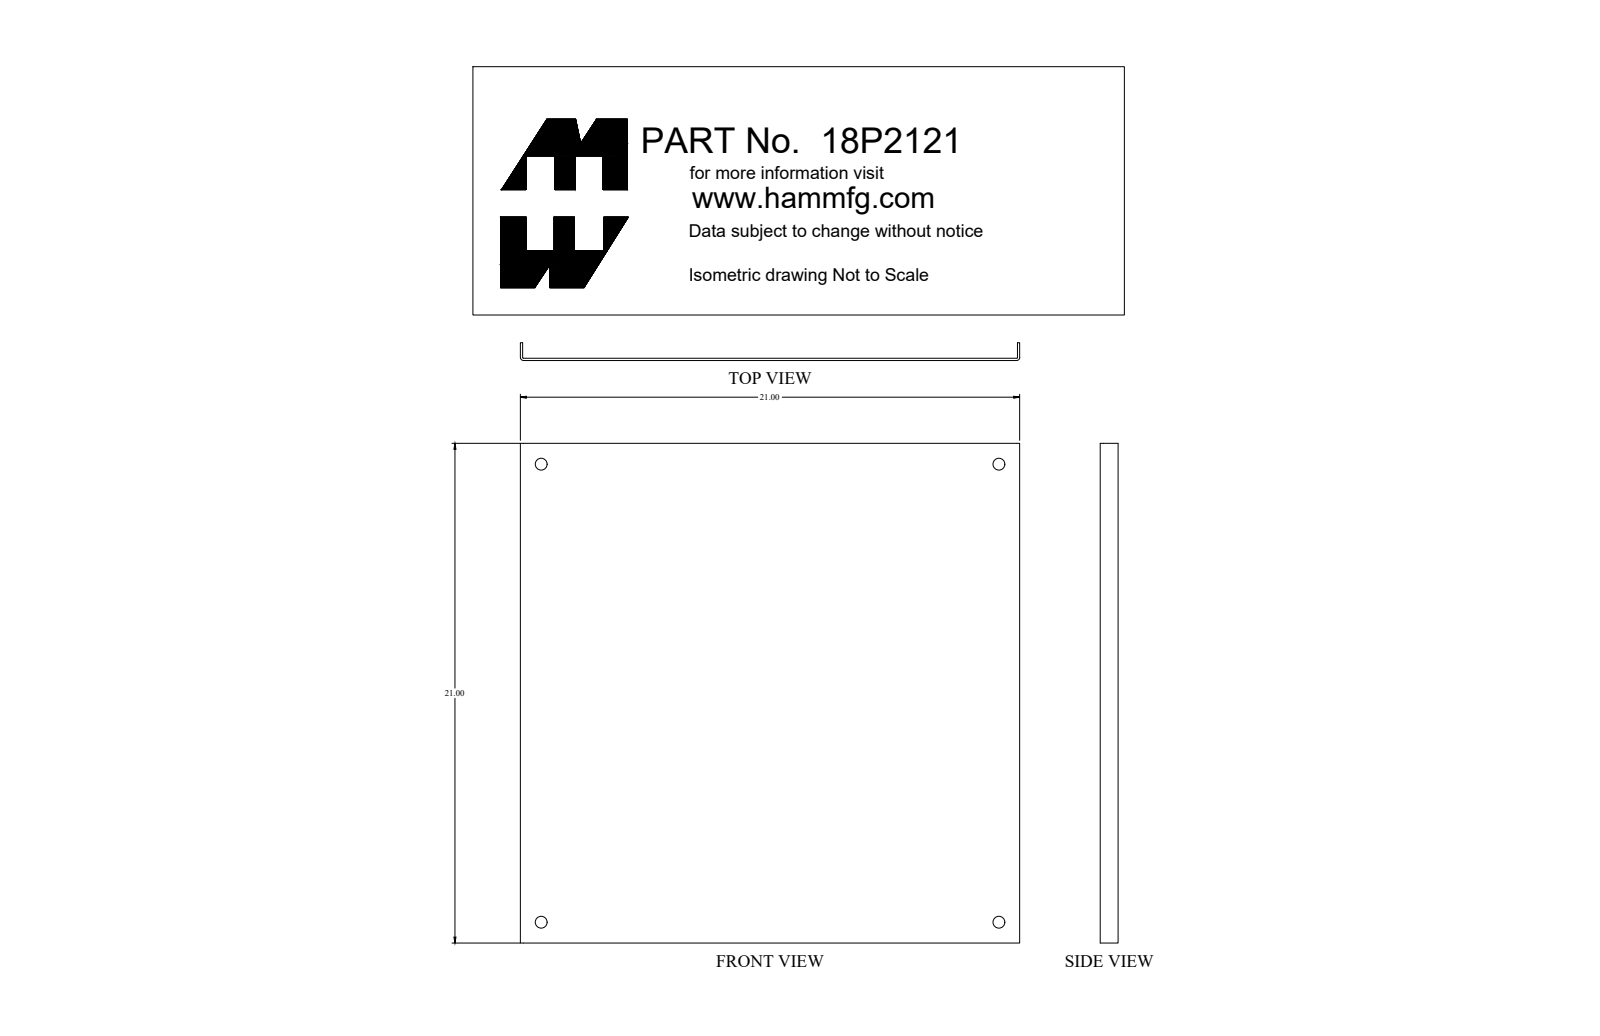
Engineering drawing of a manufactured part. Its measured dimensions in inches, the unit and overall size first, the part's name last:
Units: inches
Overall size (bounding box): 21 × 21 × 0.75
Round holes (diameter × count): ⌀0.5 ×4
Partial cylindrical surfaces — rounded edges, fillets, slot ends (radius × count): R0.03 ×2, R0.125 ×2
Main face-to-face distances: 0.095, 20.905, 21, 20.81, 0.75, 0.655
Hole centre spacings: 19.25, 27.223
Volume: 44.3 in³ · Surface area: 941.5 in²
Bodies: 1 solid, 22 faces (10 planar, 12 cylindrical, 0 other)
Part name (STEP PRODUCT): 18P2121_Default
STEP written by: SolidWorks 2018 (CONFIG_CONTROL_DESIGN)
